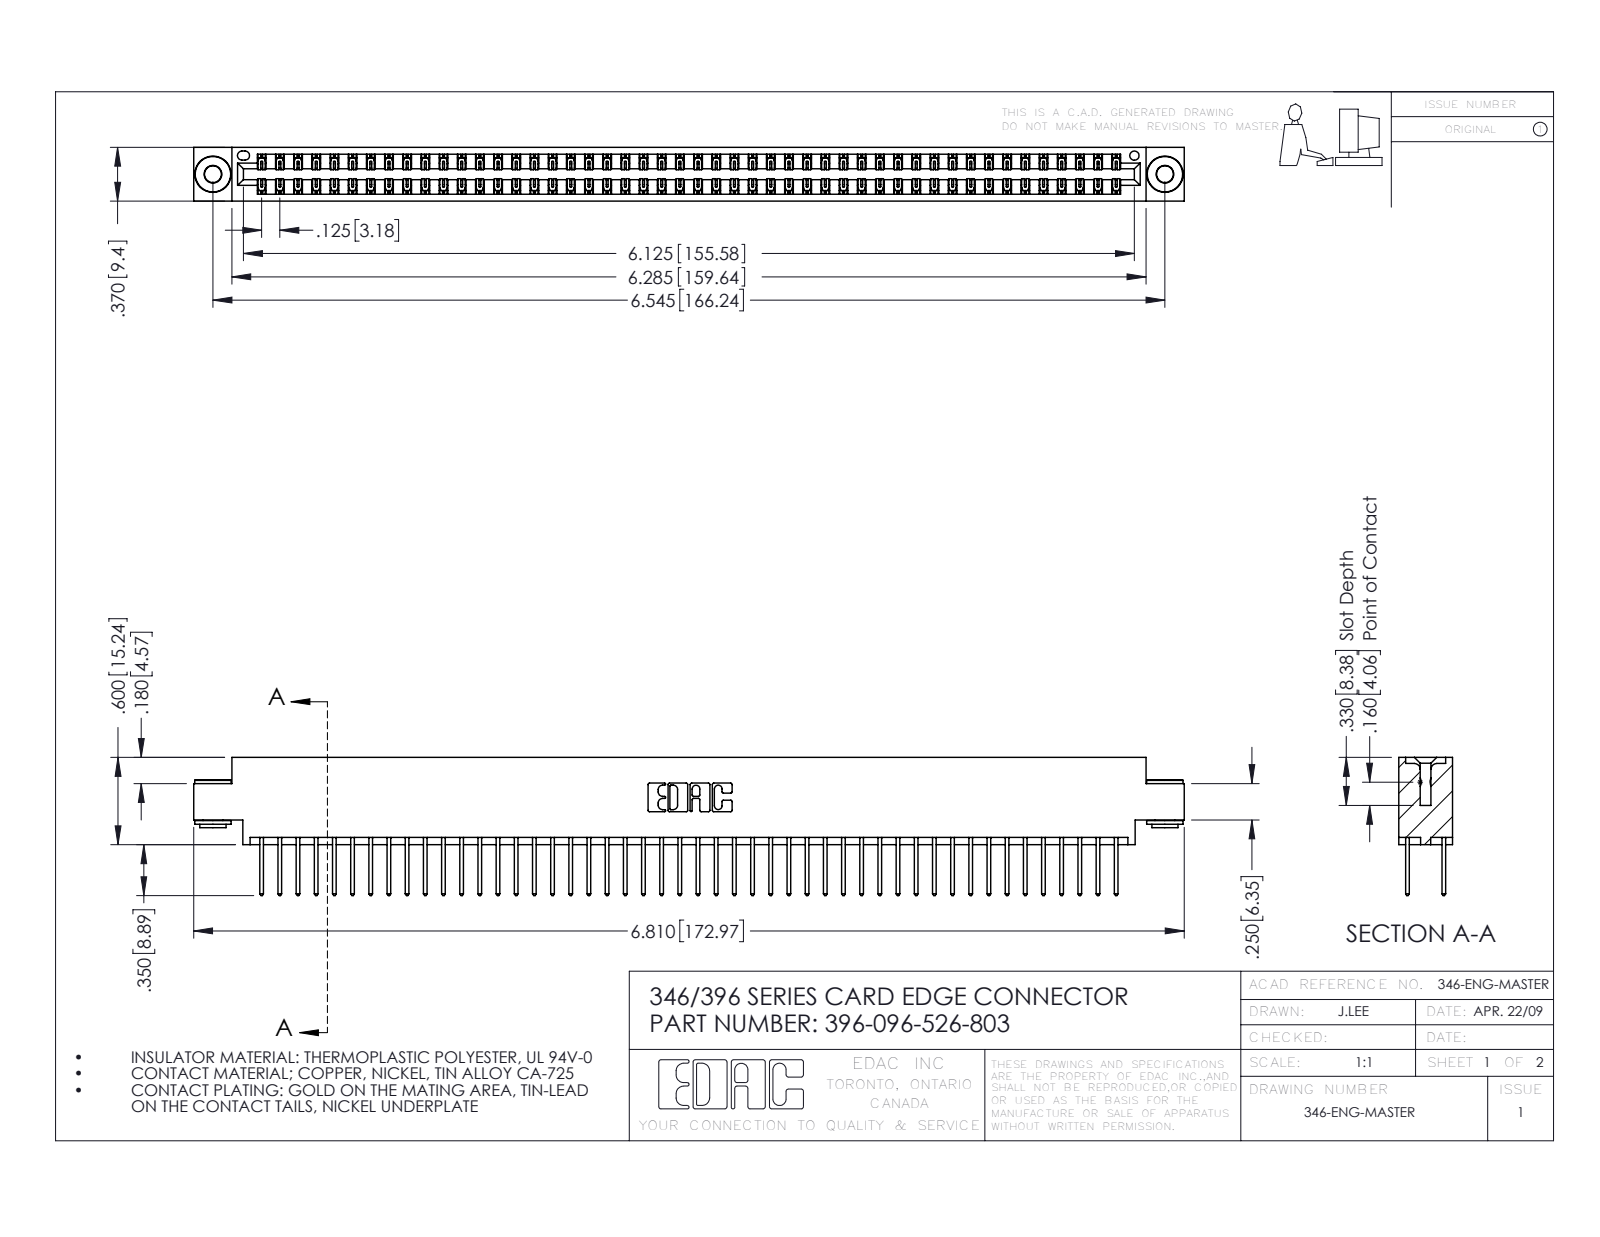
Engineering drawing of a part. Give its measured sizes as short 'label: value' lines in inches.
name: 346 Part_0.170 Offset - 0.156 Dia-TH; 345-292-001_345-293-126; 396-096-526-803; 345-250-002_345-250-002-102
written by: SolidWorks 2016 (CONFIG_CONTROL_DESIGN)
unit: in
bodies: 99 solids, 5156 faces (3450 planar, 1698 cylindrical, 8 other)
size: 6.81 × 0.95 × 0.37
volume: 1.033 in³; area: 37.93 in²
holes: 2× ⌀0.116, 2× ⌀0.156, 1× ⌀0.064
bosses: 2× ⌀0.25, 2× ⌀0.18, 2× ⌀0.136
rounds: 144× R0.006, 96× R0.01, 22× R0.01, 6× R0.007, 6× R0.031, 3× R0.026, 2× R0.014, 2× R0.022
face distances: 0.048, 0.322, 0.25, 0.37, 0.025, 0.072, 0.298, 0.275, 0.148, 0.222
hole spacings: 0.246, 6.336, 6.545
